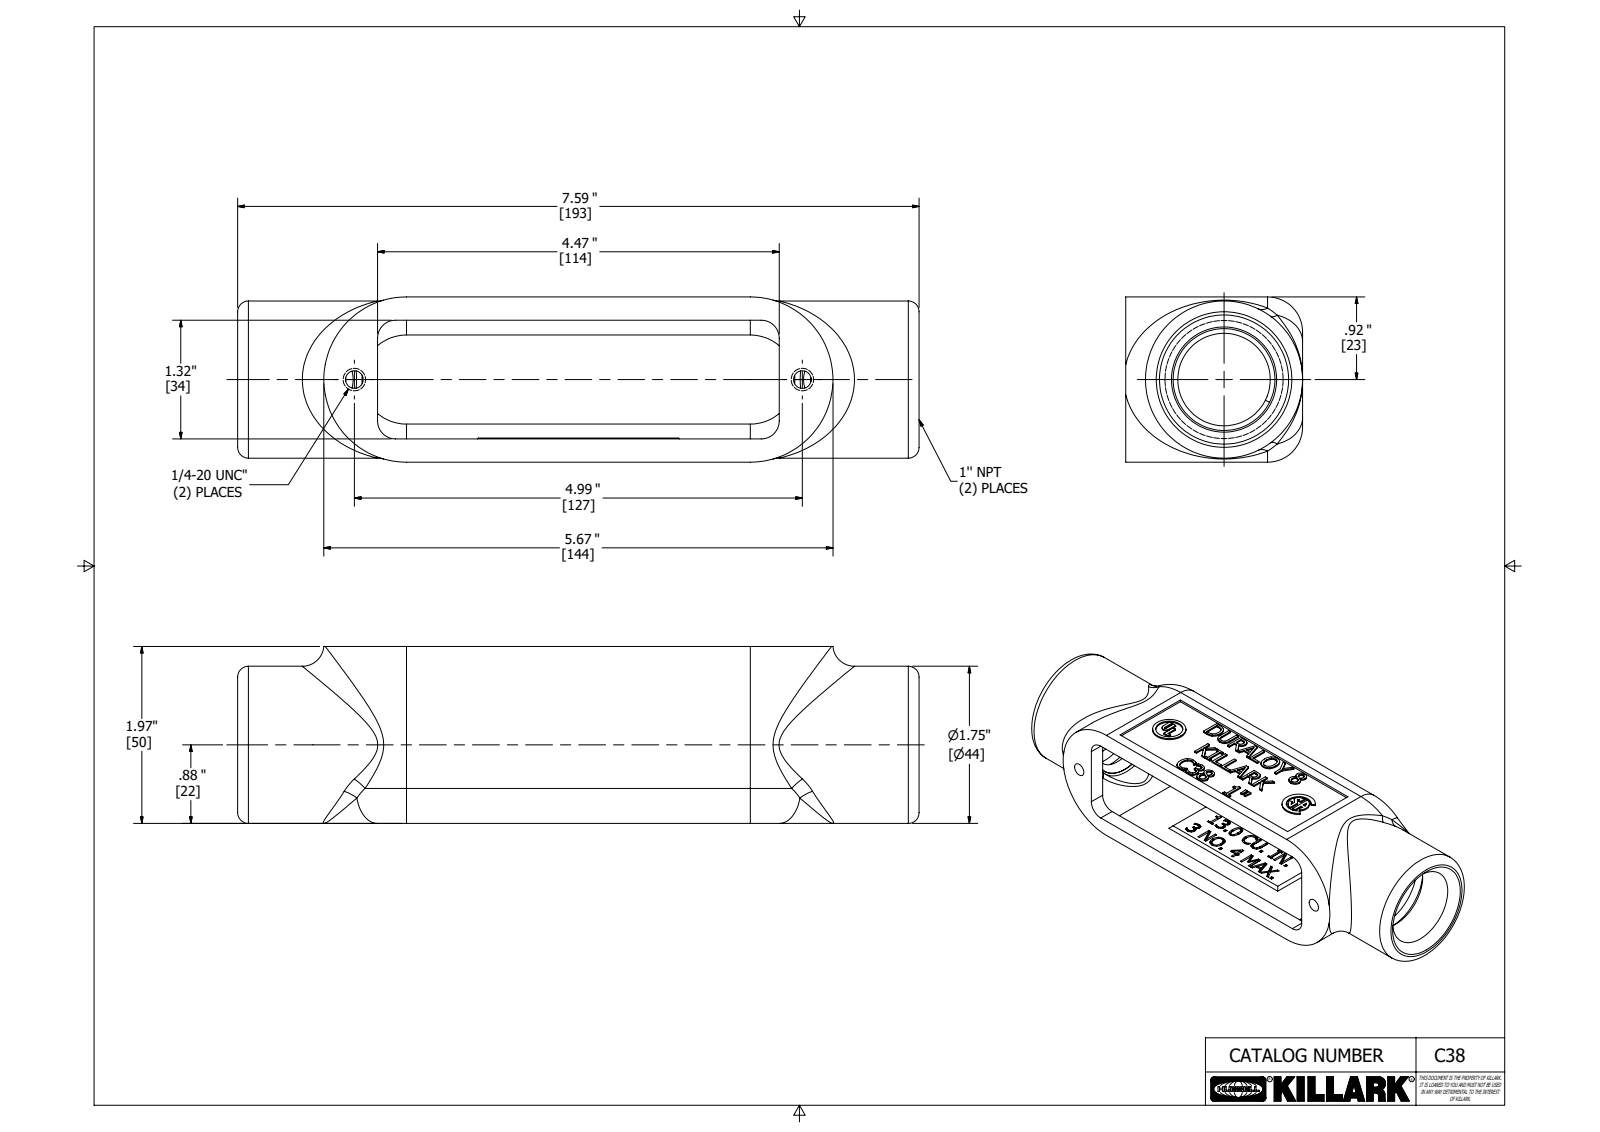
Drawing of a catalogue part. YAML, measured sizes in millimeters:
part_name: "21708-2"
step_written_by: "Autodesk Inventor 2018 (AUTOMOTIVE_DESIGN)"
units: millimeters
bodies: {solids: 1, faces: 686, planar: 401, cylindrical: 36, other: 249}
overall_size: [192.8, 50, 46.7]
volume: 153600
surface_area: 54880
round_holes:
  - {diameter: 5, count: 2}
  - {diameter: 10.3, count: 1}
  - {diameter: 33.6, count: 1}
round_bosses_or_shafts:
  - {diameter: 44.5, count: 1}
  - {diameter: 12.7, count: 1}
partial_cylinders:
  - {radius: 5.1, count: 6}
  - {radius: 9.9, count: 2}
  - {radius: 17.7, count: 2}
  - {radius: 23.4, count: 2}
  - {radius: 0.4, count: 1}
  - {radius: 1.6, count: 1}
  - {radius: 2.9, count: 1}
  - {radius: 4.1, count: 1}
face_to_face_distances: [5.7, 41, 46, 4.9, 50, 44.3, 35.4, 40.3, 0.9, 6.6]
hole_center_spacings: [126.7]
